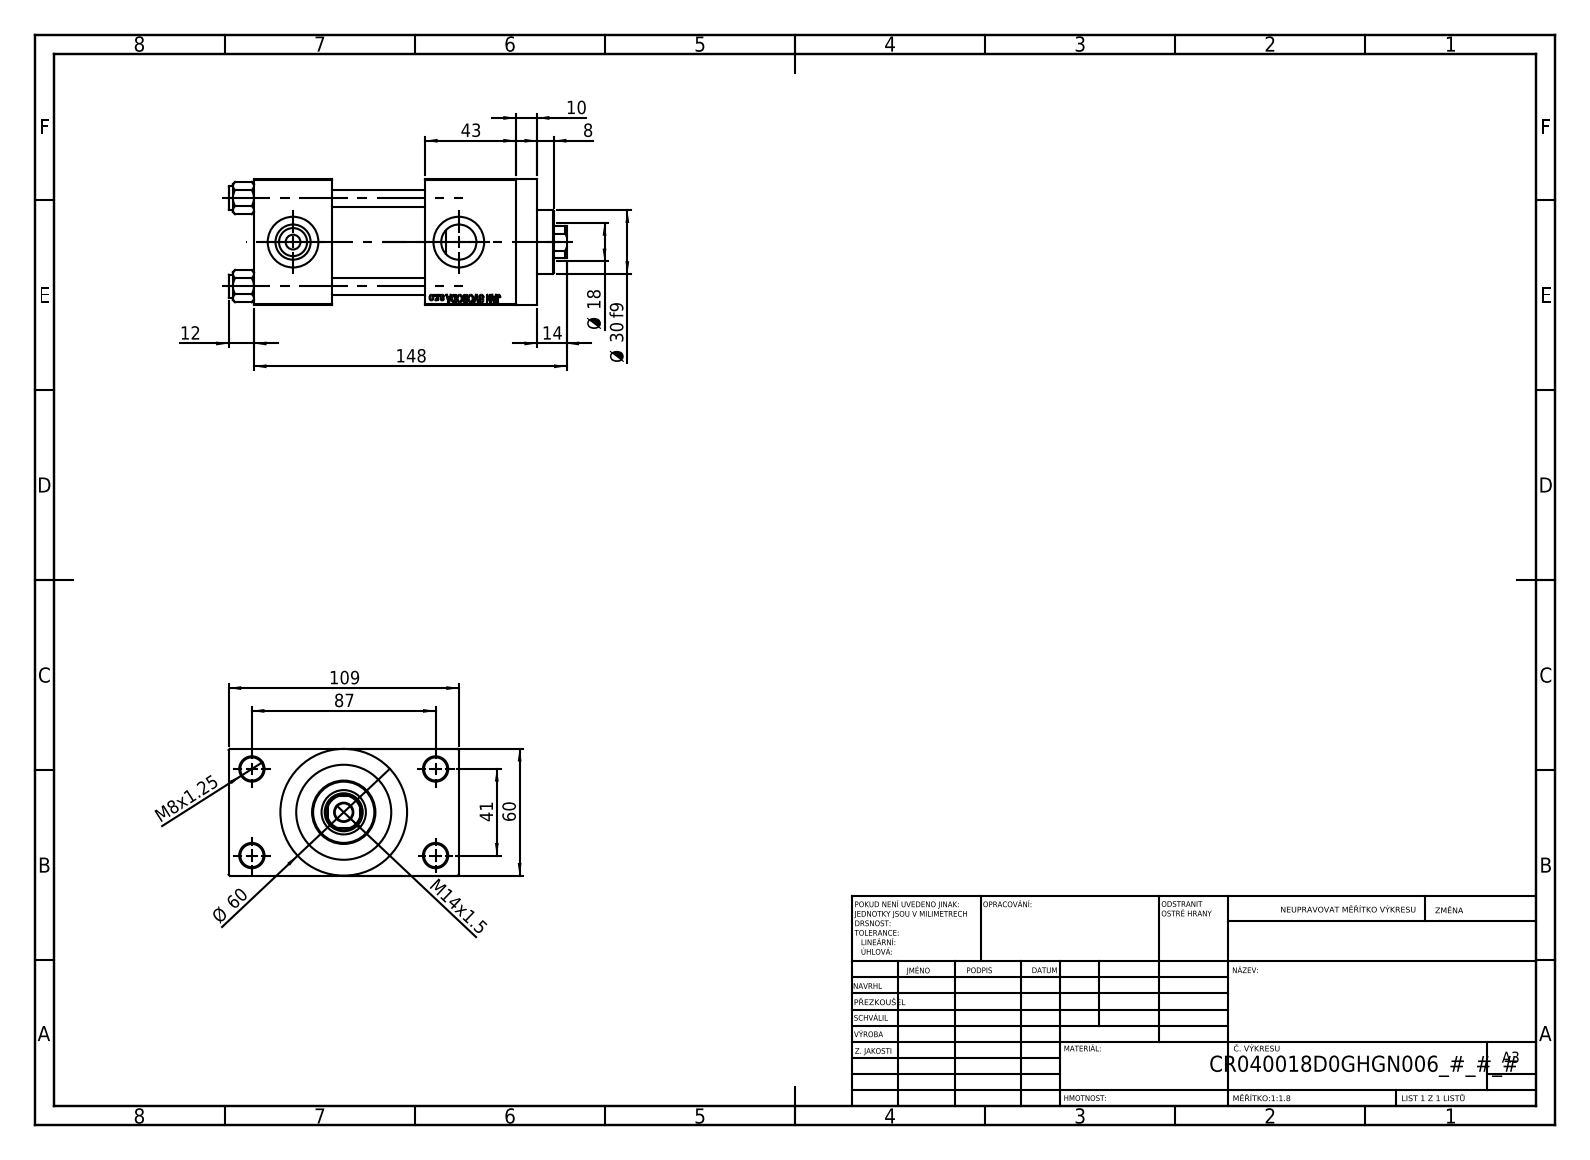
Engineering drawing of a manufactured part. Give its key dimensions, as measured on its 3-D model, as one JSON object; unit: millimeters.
{"part_name": "V215CR_D_Body; NUT_M5_D; V215_VC_A; V215CR_D_TYCINKA (+1 more)", "step_written_by": "SolidWorks 2019 (CONFIG_CONTROL_DESIGN)", "units": "millimeters", "bodies": {"solids": 11, "faces": 1104, "planar": 498, "cylindrical": 88, "other": 518}, "overall_size": [160, 109, 60], "volume_mm3": 486648, "surface_area_mm2": 115183, "round_holes": [[8, 4], [11, 4], [7, 2], [16.66, 2], [24, 2], [8.5, 1], [18, 1], [21, 1], [31, 1], [40, 1], [45, 1]], "round_bosses_or_shafts": [[11, 4], [60, 1], [46, 1], [30, 1]], "partial_cylinders_radius": [[8.5, 1]], "face_to_face_distances": [60, 44, 24.5, 84.5, 37, 81, 124, 87, 43, 10], "hole_center_spacings": [22.65, 29.49, 41.7, 47.15, 48.09, 64.35, 76.49, 41]}
